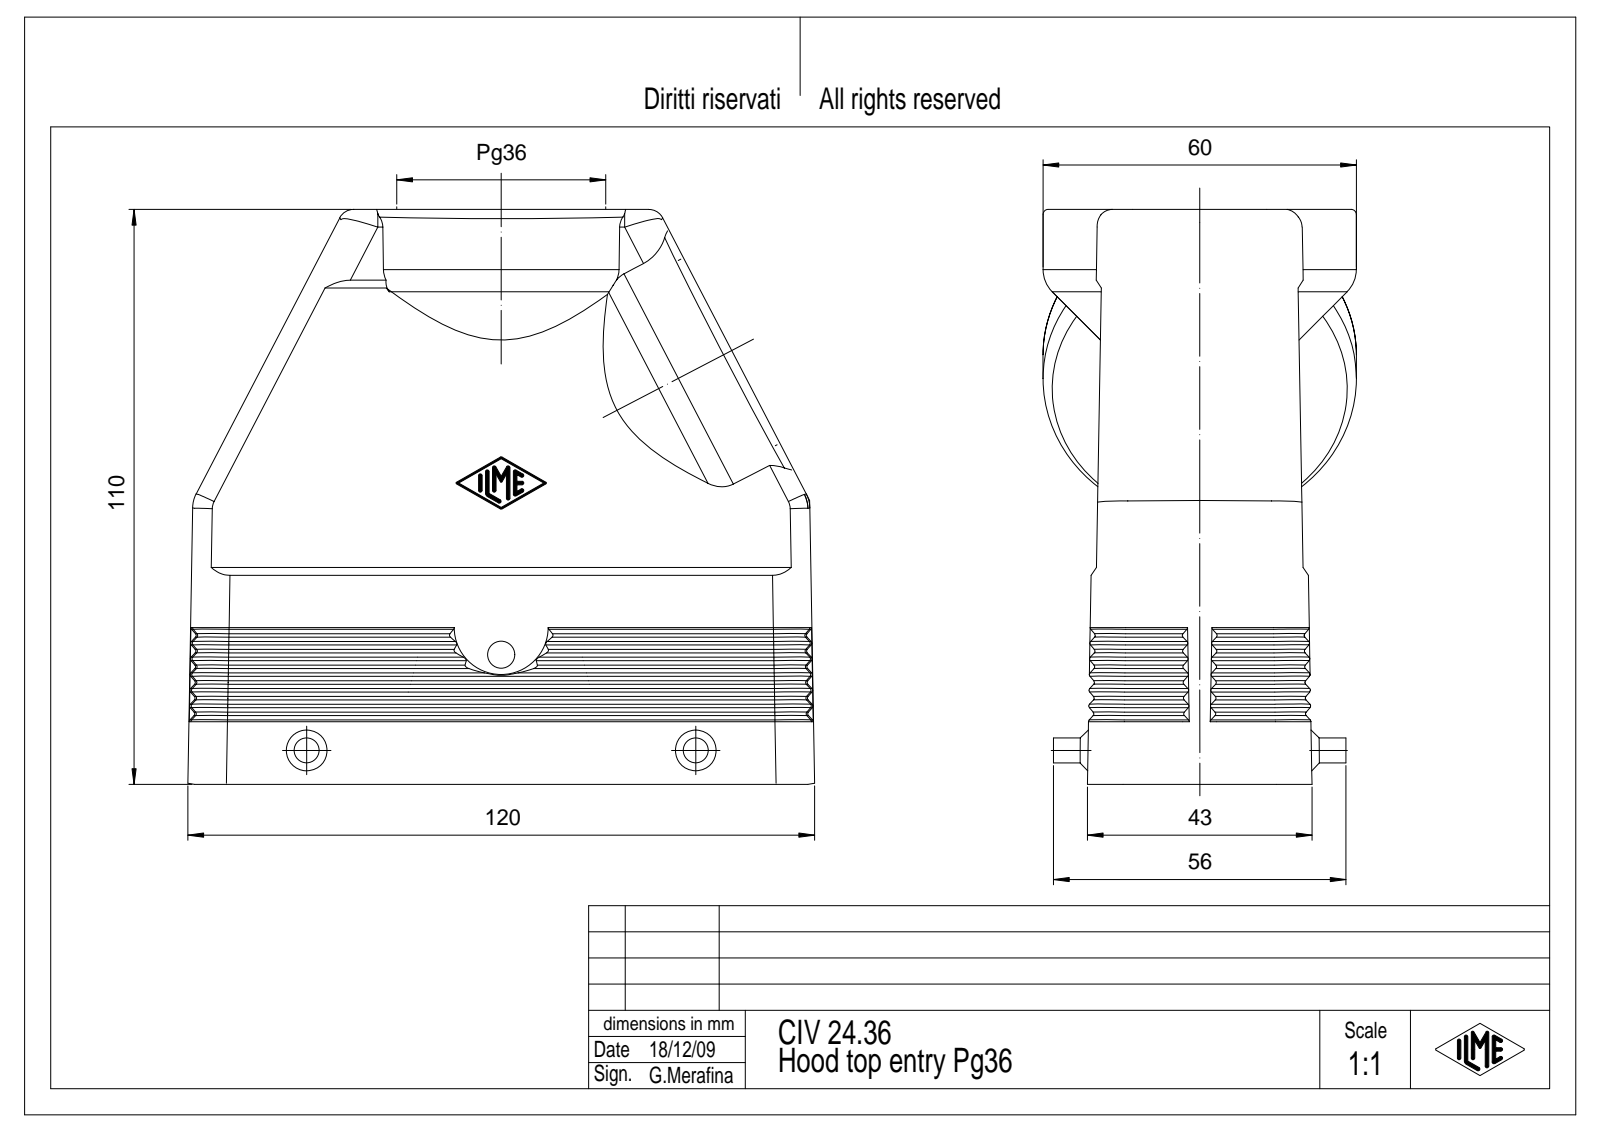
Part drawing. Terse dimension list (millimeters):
name: CIV_24.36
written by: CoCreate Modeling 16.00A 16-Aug-2008 (C) Parametric Technology GmbH (AUTOMOTIVE_DESIGN)
unit: mm
bodies: 1 solid, 568 faces (204 planar, 199 cylindrical, 165 other)
size: 119.23 × 109.2 × 60
volume: 108 478 mm³; area: 66 365 mm²
holes: 4× ⌀3.5, 1× ⌀5.2, 1× ⌀47
bosses: 2× ⌀4.8
rounds: 78× R0.5, 10× R3, 8× R7, 4× R4.2, 2× R30, 2× R33.77, 1× R1
face distances: 1.05, 2, 5.58, 2.39, 7.95, 4, 8.5, 3.99, 5.99, 7.99
hole spacings: 53.72, 27, 104, 107.45
